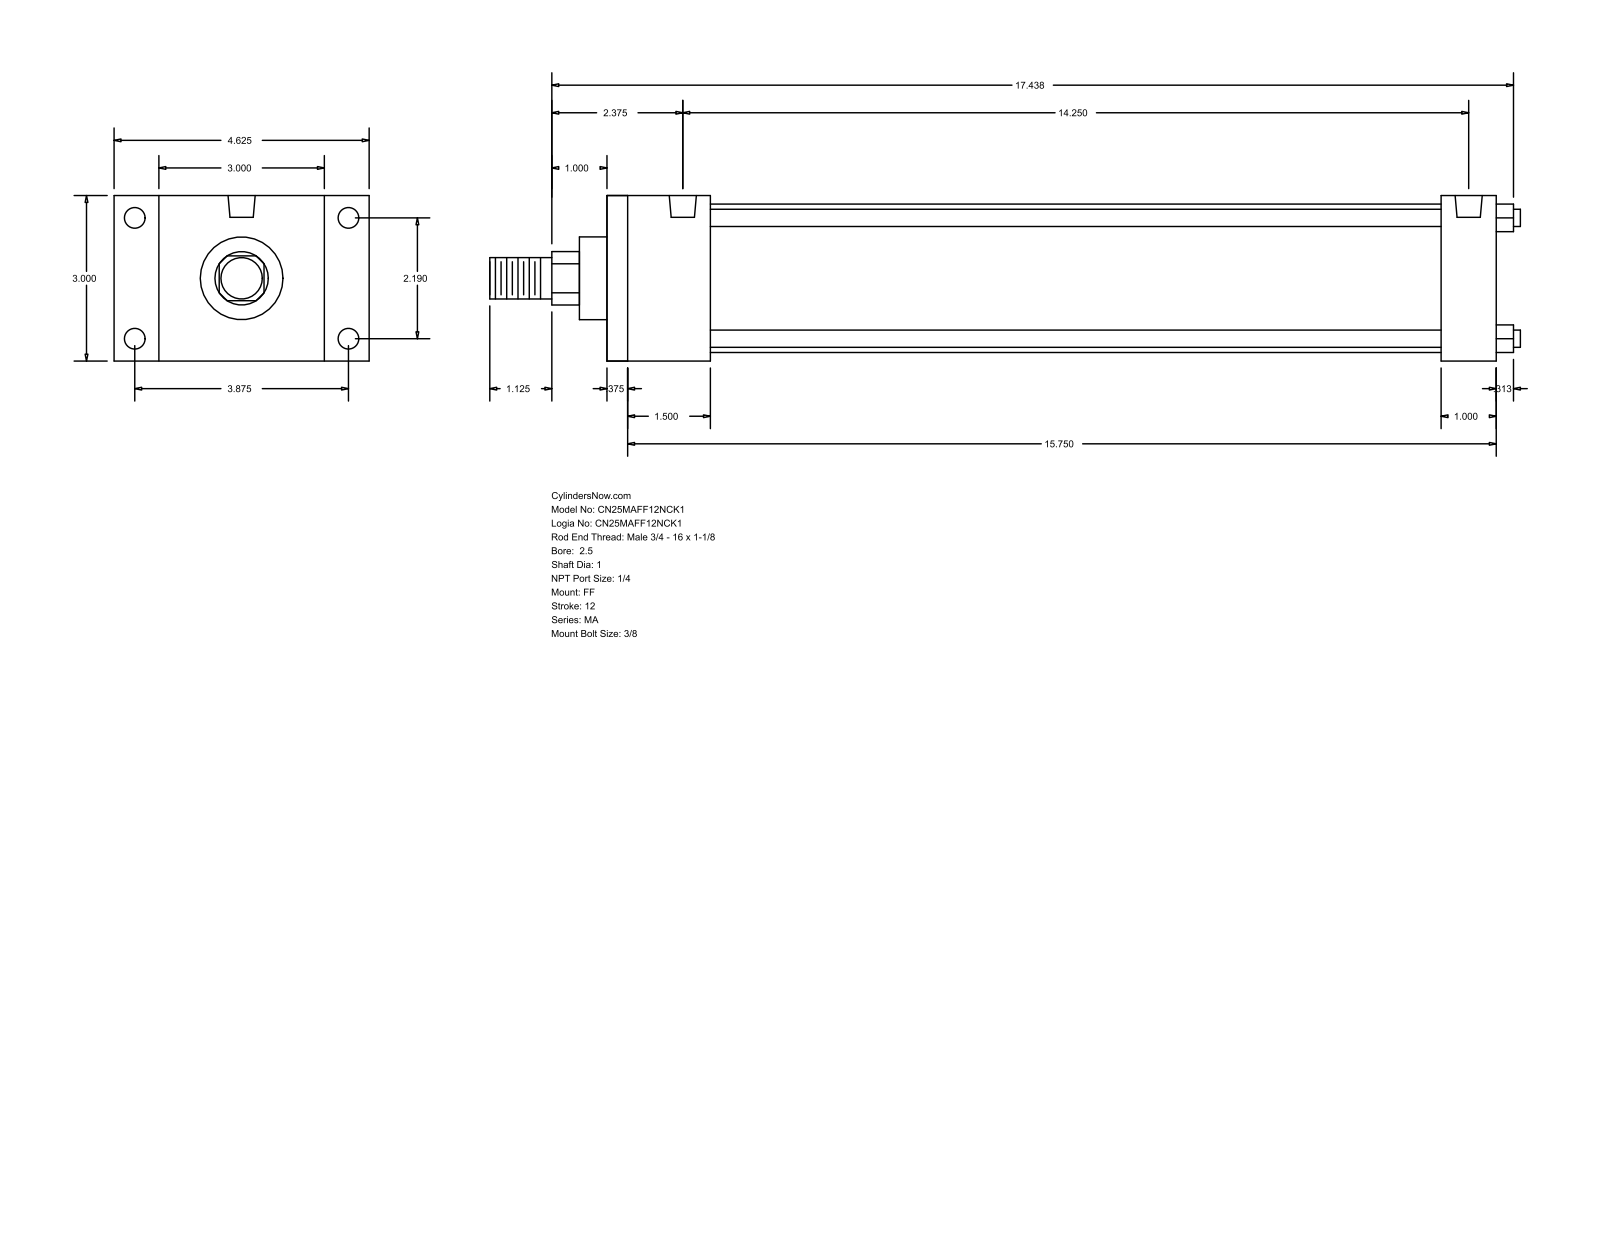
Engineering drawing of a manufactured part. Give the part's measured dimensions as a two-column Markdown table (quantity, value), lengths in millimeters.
| quantity | value |
| --- | --- |
| part name | MA_FF__0250_1 |
| STEP written by | GSSL Pune (CONFIG_CONTROL_DESIGN) |
| units | millimeters |
| bodies | 0 solids, 92 faces (64 planar, 28 cylindrical, 0 other) |
| overall size | 474.66 × 117.47 × 76.2 |
| round holes (diameter × count) | 7.94 × 4, 9.53 × 4, 12.49 × 2 |
| round bosses / shafts (diameter × count) | 7.94 × 4, 68.33 × 1, 38.1 × 1, 25.4 × 1, 19.05 × 1 |
| partial cylindrical surfaces (radius × count) | 12.29 × 1 |
| main face-to-face distances | 76.2, 409.58, 9.52, 400.06, 47.63, 384.17, 38.11, 374.65, 336.54, 361.95 |
| hole center spacings | 55.62, 98.42, 113.05, 361.94 |
